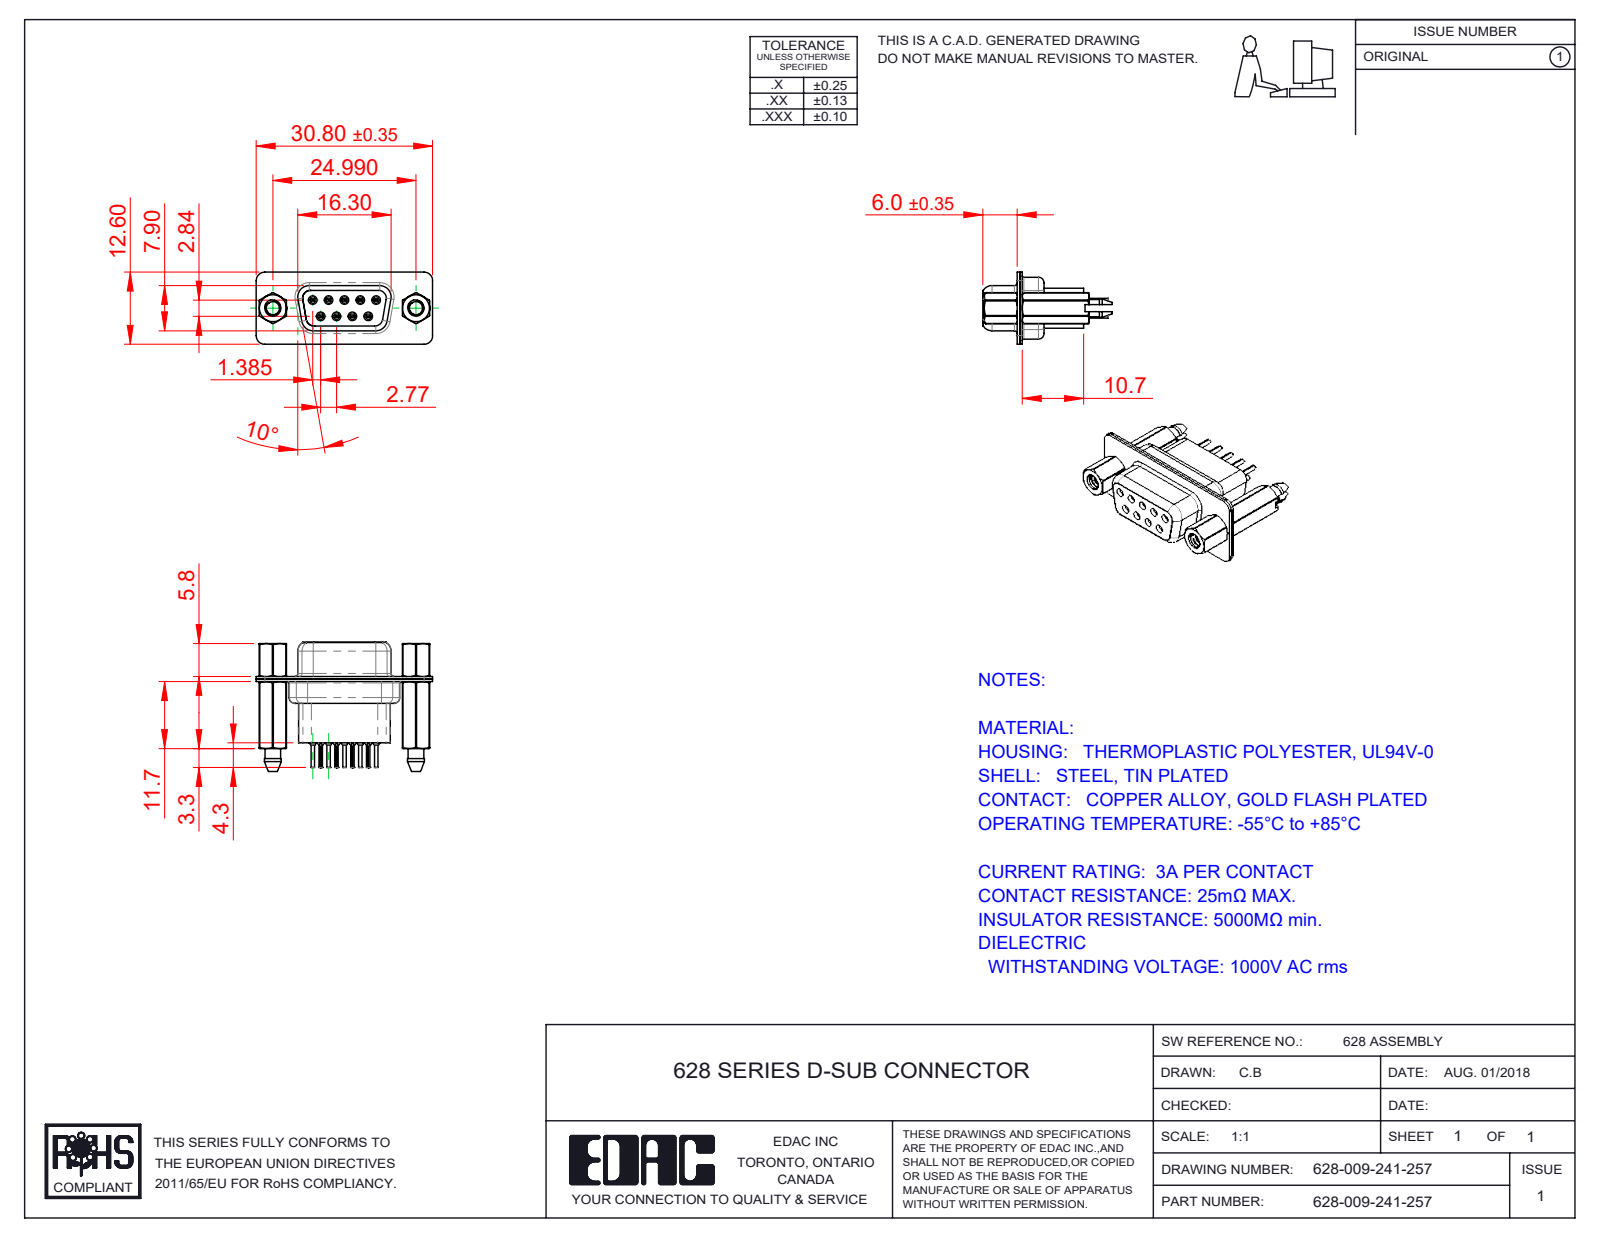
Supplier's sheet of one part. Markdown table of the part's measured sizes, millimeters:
| quantity | value |
| --- | --- |
| part name | 628-009-241-257; 628 4-40 Threaded Boardlock_HP41; 628 4-40 Hex Standoff; 628 Shell Rear_09 Contacts (+4 more) |
| STEP written by | SolidWorks 2020 (CONFIG_CONTROL_DESIGN) |
| units | millimeters |
| bodies | 16 solids, 1586 faces (400 planar, 538 cylindrical, 648 other) |
| overall size | 30.8 × 22.6 × 12.6 |
| volume | 2 737 mm³ |
| surface area | 6 376 mm² |
| round holes (diameter × count) | 0.2 × 9, 0.8 × 9, 0.9 × 9, 1.1 × 9, 1.6 × 9, 1.7 × 5, 2.26 × 2, 2.29 × 2, 4 × 2, 4.05 × 2, 4.85 × 2 |
| round bosses / shafts (diameter × count) | 2 × 9, 1.5 × 9, 1.2 × 9, 0.6 × 9, 4.95 × 2, 4.8 × 2, 2.79 × 2 |
| partial cylindrical surfaces (radius × count) | 1.5 × 19, 0.1 × 18, 2 × 12, 0.28 × 9, 1.35 × 6, 1.6 × 6, 0.25 × 4, 0.5 × 4 |
| main face-to-face distances | 0.45, 0.4, 0.9, 8.5, 4.76, 6.6, 1.9, 1.4, 7, 0.5 |
| hole center spacings | 3.16, 2.77, 5.54, 5.03, 5.04, 8.31, 7.48, 7.49 |
